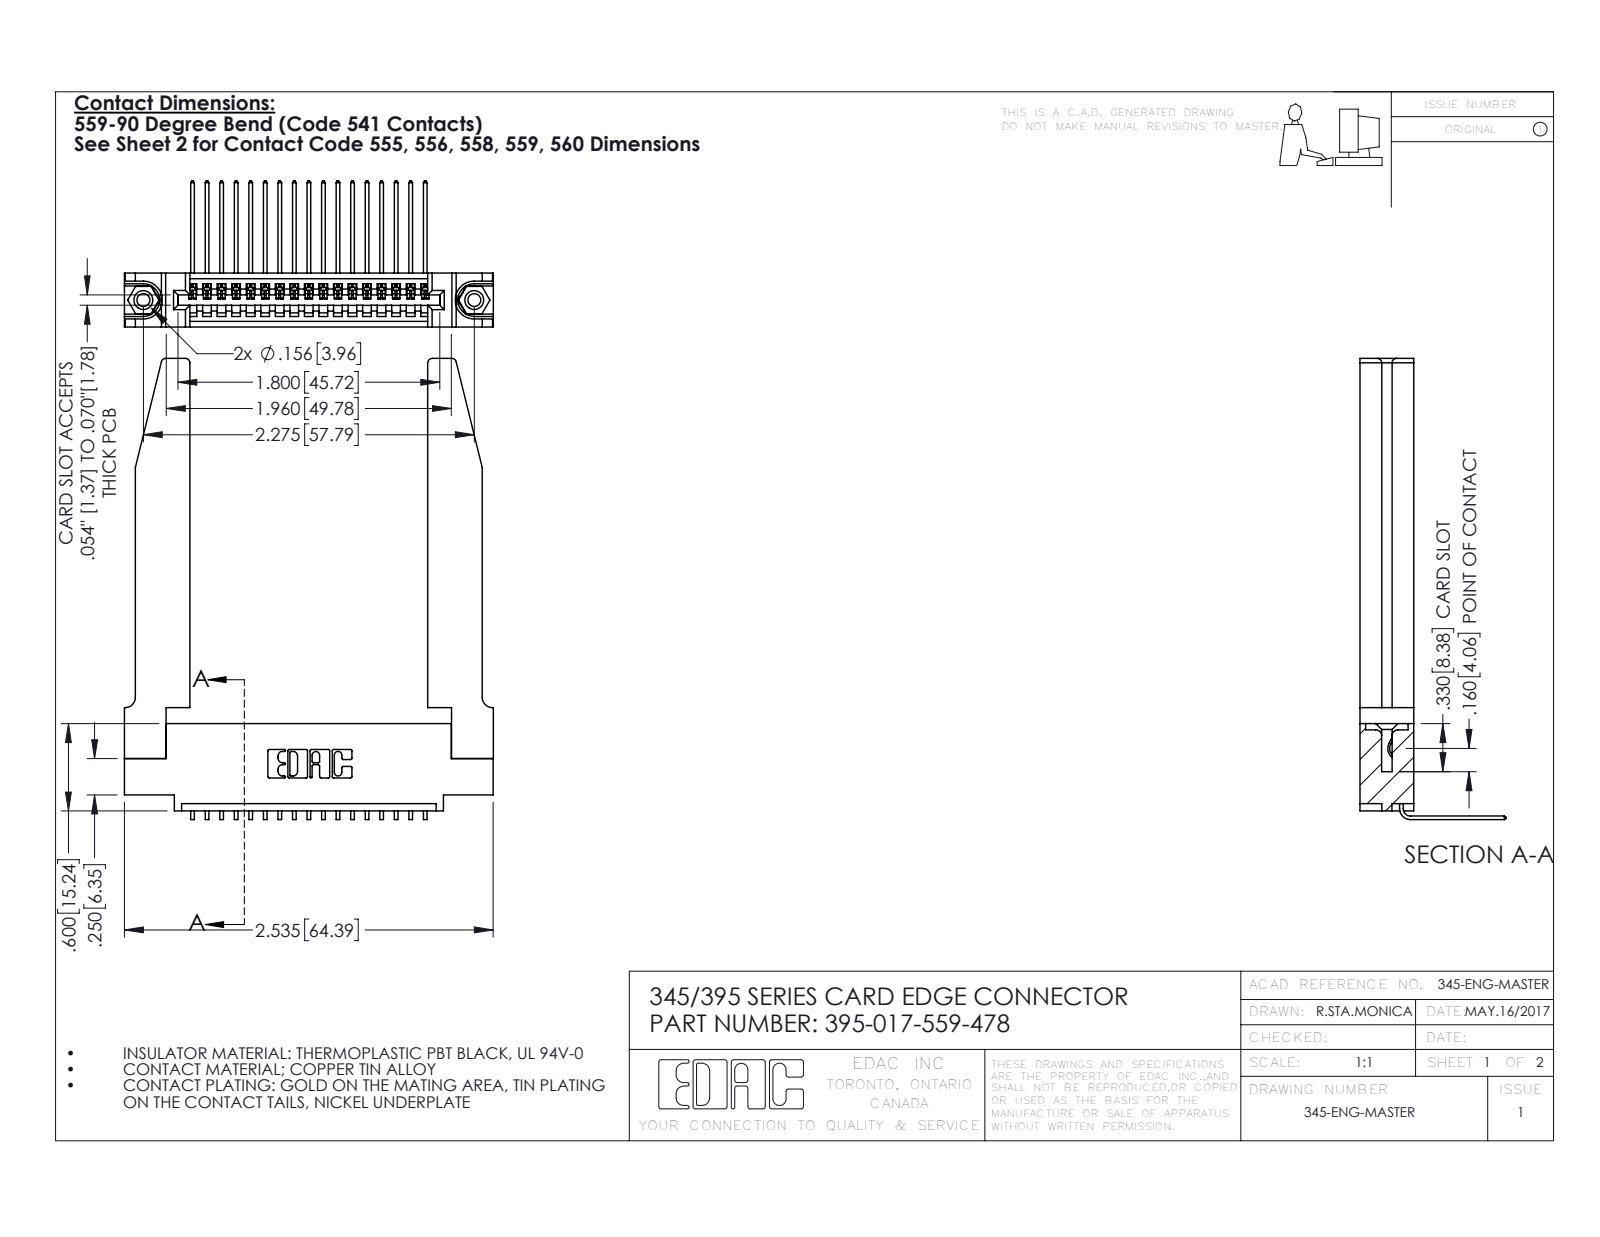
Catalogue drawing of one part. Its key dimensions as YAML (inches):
part_name: "345-220-078_345-220-078; 345 Part_0.110 Offset - 0.156 Dia-TH; 395-017-559-478; 345-292-001_558 559 Tail - 1 (+1 more)"
step_written_by: "SolidWorks 2016 (CONFIG_CONTROL_DESIGN)"
units: inches
bodies: {solids: 22, faces: 1384, planar: 940, cylindrical: 392, other: 52}
overall_size: [3.169, 2.536, 1.005]
volume: 0.834
surface_area: 22.87
round_holes:
  - {diameter: 0.089, count: 2}
  - {diameter: 0.125, count: 2}
  - {diameter: 0.156, count: 2}
  - {diameter: 0.064, count: 1}
round_bosses_or_shafts:
  - {diameter: 0.155, count: 2}
partial_cylinders:
  - {radius: 0.006, count: 34}
  - {radius: 0.01, count: 22}
  - {radius: 0.03, count: 8}
  - {radius: 0.007, count: 6}
  - {radius: 0.031, count: 6}
  - {radius: 0.026, count: 3}
  - {radius: 0.031, count: 2}
  - {radius: 0.04, count: 2}
face_to_face_distances: [0.37, 0.072, 0.298, 0.148, 0.15, 0.2, 0.22, 0.077, 0.098, 0.272]
hole_center_spacings: [0.27, 2.041, 2.275]
